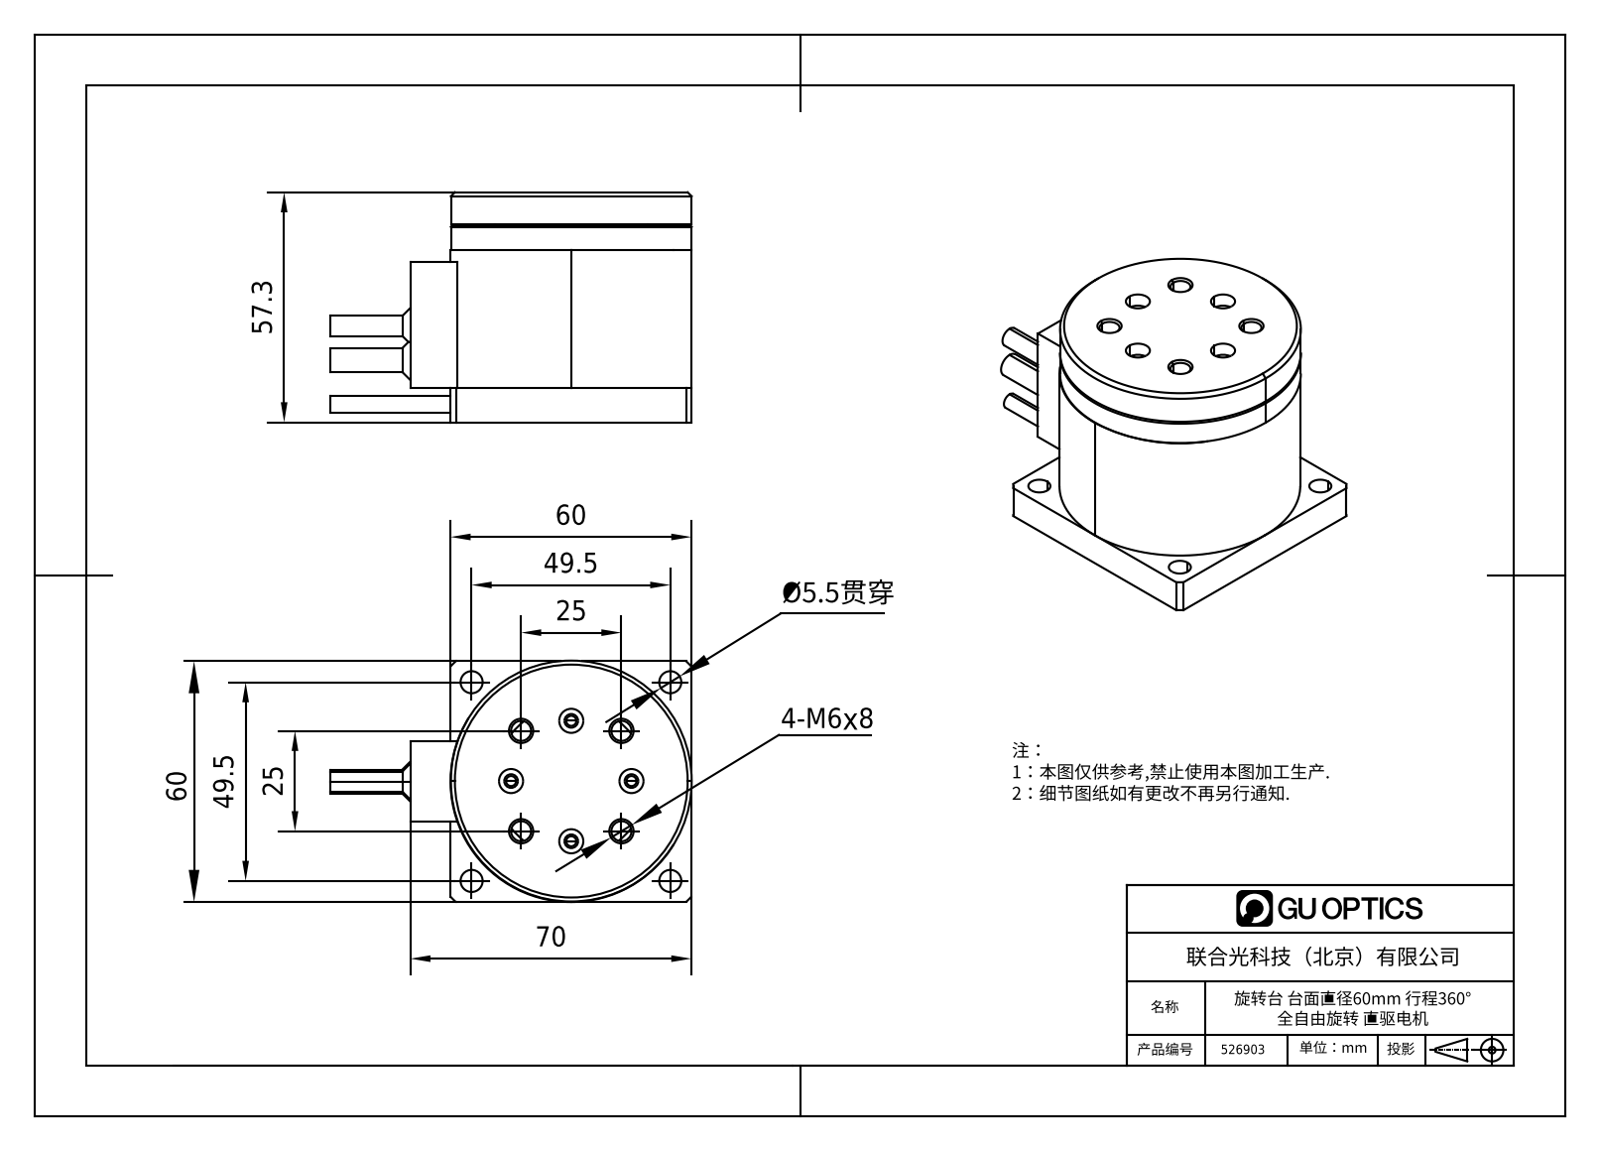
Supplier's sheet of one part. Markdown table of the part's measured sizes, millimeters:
| quantity | value |
| --- | --- |
| part name | FMSR60D |
| STEP written by | SolidWorks 2017 (AUTOMOTIVE_DESIGN) |
| units | millimeters |
| bodies | 3 solids, 213 faces (88 planar, 99 cylindrical, 26 other) |
| overall size | 90.08 × 60.13 × 57.3 |
| volume | 170 150 mm³ |
| surface area | 38 273 mm² |
| round holes (diameter × count) | 6 × 7, 2.5 × 4, 3.4 × 4, 5 × 4, 5.5 × 4, 4 × 3, 22 × 2, 37 × 1, 38 × 1, 57.4 × 1 |
| round bosses / shafts (diameter × count) | 5.6 × 3, 3.8 × 3, 60 × 2, 56.4 × 1, 20 × 1, 6 × 1, 5 × 1, 4 × 1 |
| partial cylindrical surfaces (radius × count) | 41.5 × 1 |
| main face-to-face distances | 40.8, 8.5, 8.2, 57.3, 16.5, 41, 16.3, 8.9, 0.4, 40.7 |
| hole center spacings | 12.75, 30.21, 15, 25, 17.68, 21.21, 35, 49.5 |
